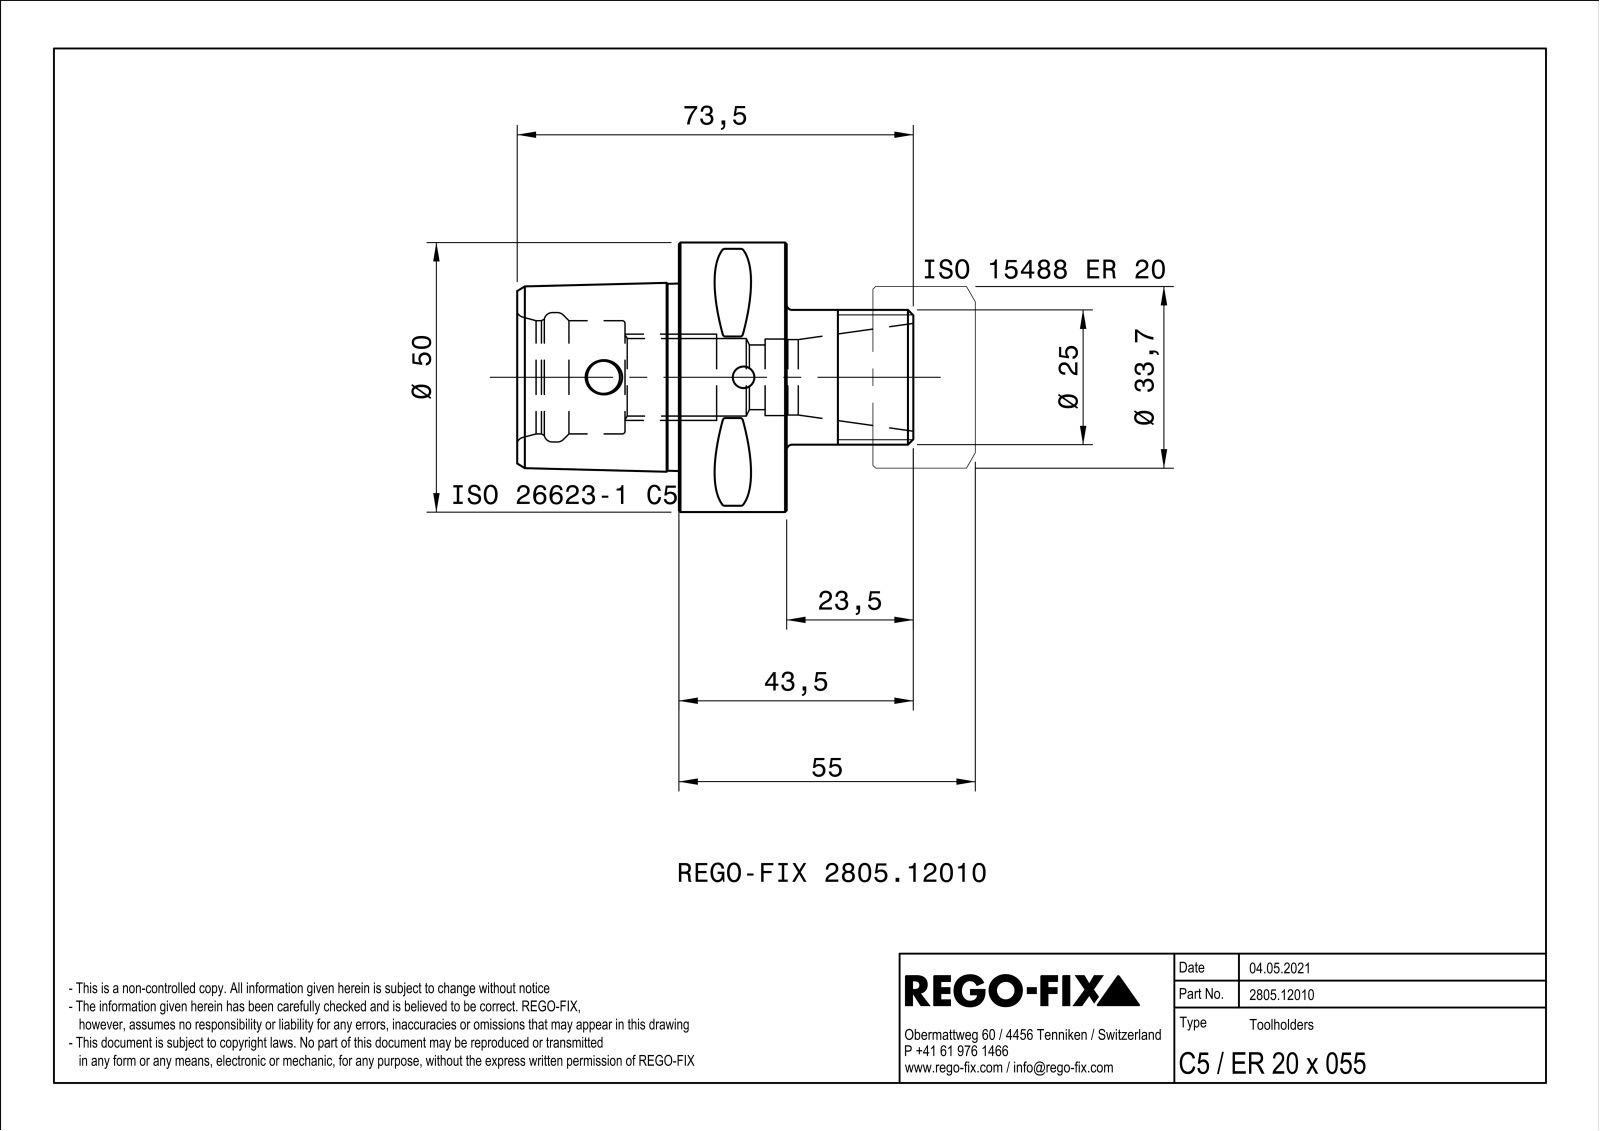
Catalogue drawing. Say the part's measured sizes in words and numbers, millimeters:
The part is named "NOCUT". Its 3-D file was written by "SIEMENS PLM Software Solid Edge ST10 (AUTOMOTIVE_DESIGN)". It is 1 solid with 98 faces: 21 planar, 23 cylindrical and 54 other. Overall it measures 73.5 by 50 by 50 millimeters. Its volume is 59 384 cubic millimeters and its surface area 15 780 square millimeters. Round holes: 1 of diameter 4, 1 of diameter 6.1, 1 of diameter 12, 1 of diameter 14, 1 of diameter 14.2, 1 of diameter 14.38, 1 of diameter 21, 1 of diameter 24. Round bosses or shafts: 1 of diameter 50, 1 of diameter 25. Partial cylindrical surfaces (rounded edges, fillets, slot ends): 8 of radius 0.5, 1 of radius 4. The main face-to-face distances are 20, 30, 50, 19.18, 44.4, 10, 23.5, 43.5, 53.5, 73.5. The hole center spacings are 26.
